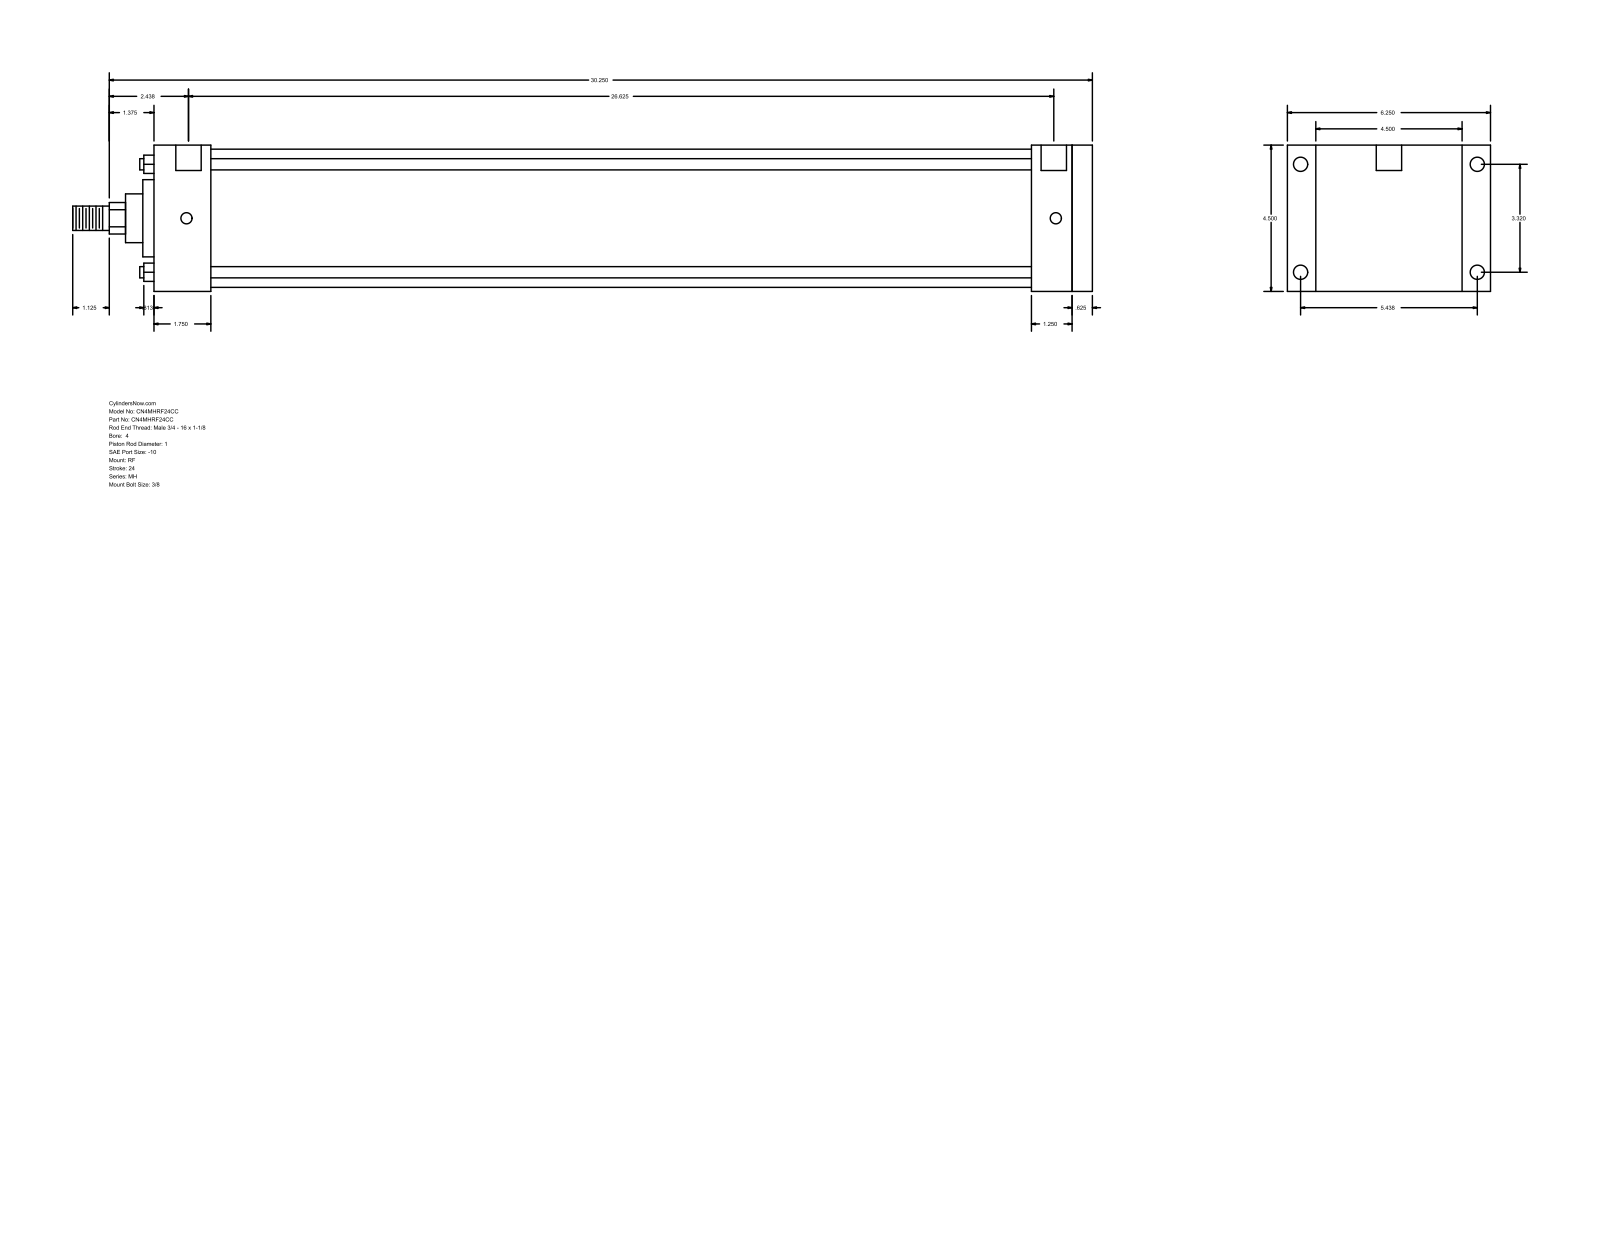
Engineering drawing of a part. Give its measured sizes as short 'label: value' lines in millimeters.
name: MH_RF__0400_1
written by: GSSL Pune (CONFIG_CONTROL_DESIGN)
unit: mm
bodies: 0 solids, 94 faces (65 planar, 29 cylindrical, 0 other)
size: 796.92 × 158.75 × 114.3
holes: 4× ⌀8.73, 4× ⌀11.13, 2× ⌀19.84
bosses: 4× ⌀8.76, 1× ⌀107.95, 1× ⌀60.33, 1× ⌀38.1, 1× ⌀25.4, 1× ⌀19.05
rounds: 1× R12.29
face distances: 114.3, 733.43, 717.56, 15.87, 44.46, 673.1, 688.97, 685.81, 641.35, 31.75
hole spacings: 1.58, 84.32, 138.12, 161.82, 677.86, 679.44, 676.28
